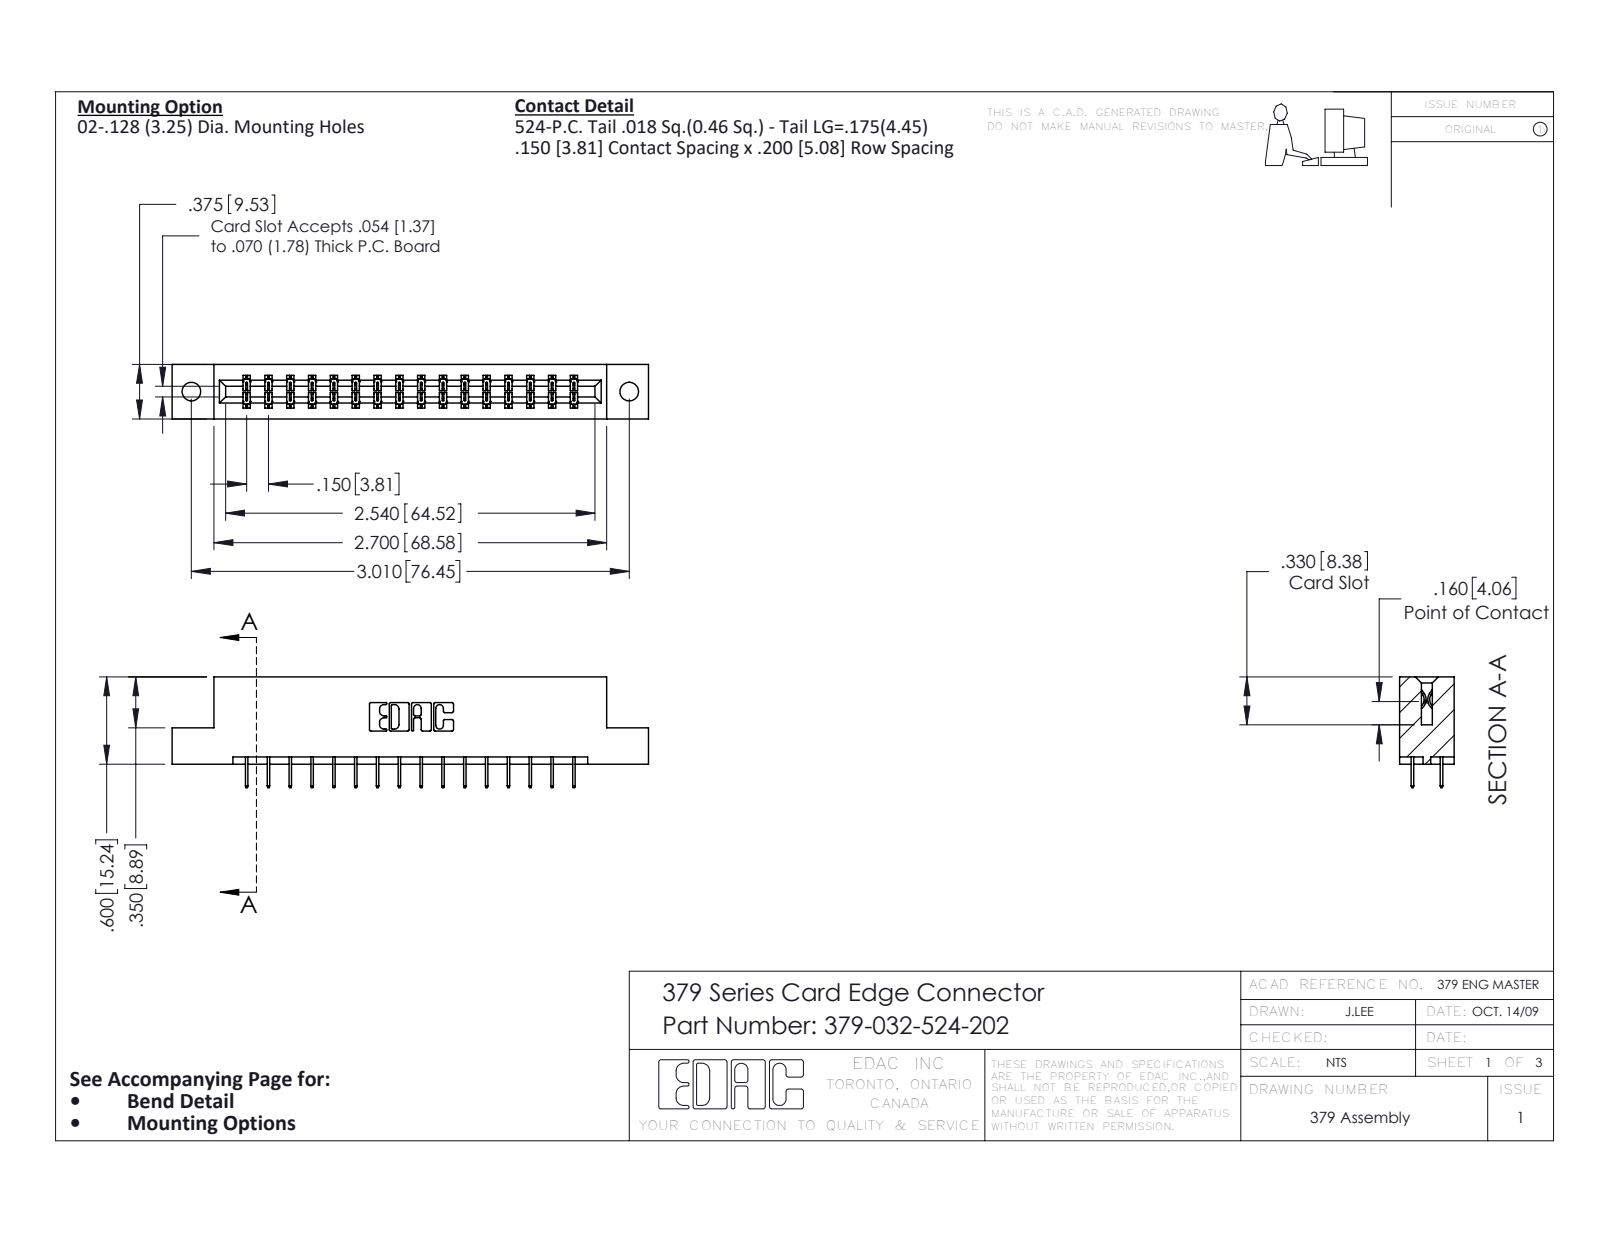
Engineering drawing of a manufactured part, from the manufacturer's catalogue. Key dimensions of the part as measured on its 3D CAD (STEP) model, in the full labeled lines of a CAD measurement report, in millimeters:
Part name (STEP PRODUCT): 379-032-524-202; 379 Part_Flush - .128 Dia; 345-292-001_345-293-124
STEP written by: SolidWorks 2020 (CONFIG_CONTROL_DESIGN)
Units: millimetres
Bodies: 33 solids, 1906 faces (1414 planar, 492 cylindrical, 0 other)
Overall size (bounding box): 83.2 × 19.4 × 9.5
Volume: 8 460 mm³ · Surface area: 8 826 mm²
Round holes (diameter × count): ⌀3.3 ×2
Partial cylindrical surfaces — rounded edges, fillets, slot ends (radius × count): R0.2 ×48, R0.3 ×22, R0.2 ×6, R0.8 ×6, R0.7 ×3, R0.4 ×2, R0.6 ×2, R0.6 ×2
Main face-to-face distances: 7.6, 9.5, 1.9, 15.2, 5.1, 3.8, 5.7, 11.4, 14, 2.5
Hole centre spacings: 76.5
